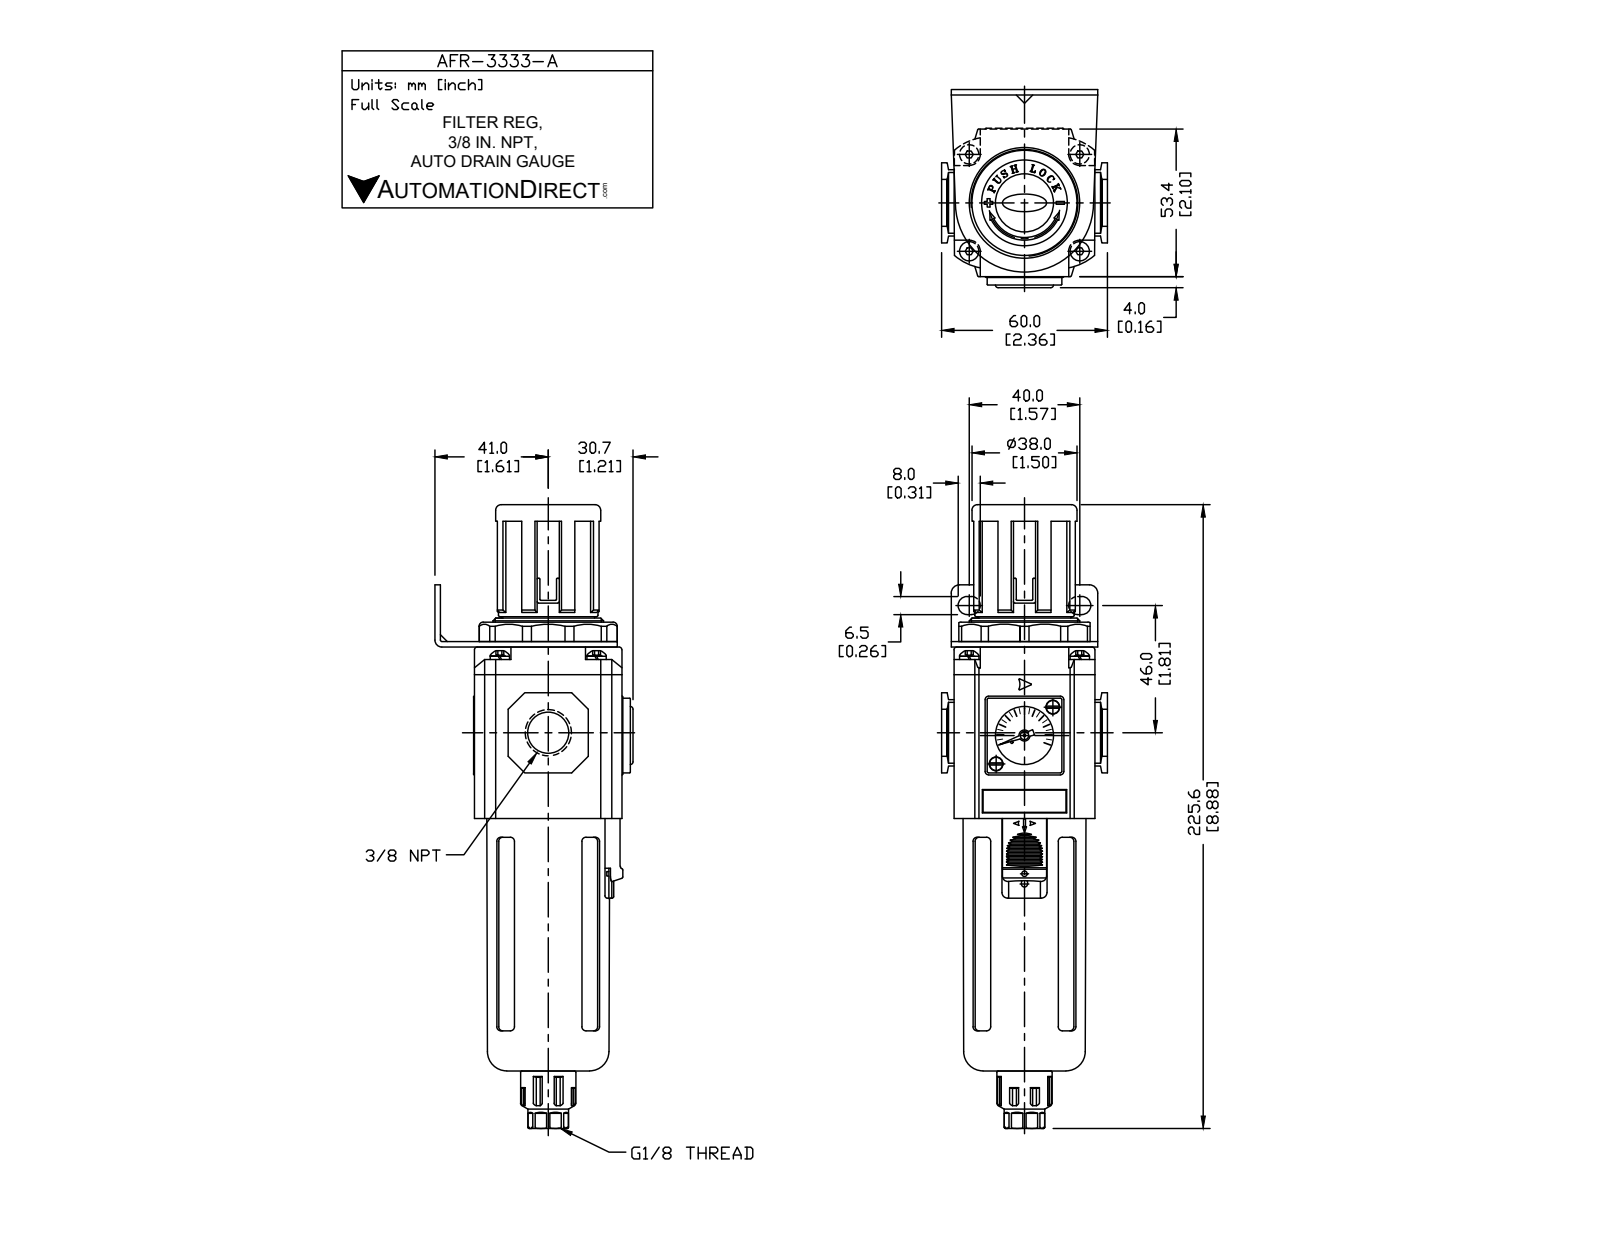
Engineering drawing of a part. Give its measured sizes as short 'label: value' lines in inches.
name: AFR-3333-A
written by: SolidWorks 2015 (CONFIG_CONTROL_DESIGN)
unit: in
bodies: 16 solids, 606 faces (370 planar, 172 cylindrical, 64 other)
size: 8.882 × 2.835 × 2.362
volume: 16.68 in³; area: 108.8 in²
holes: 6× ⌀0.118, 1× ⌀0.079, 1× ⌀0.244, 1× ⌀0.562, 1× ⌀0.63, 1× ⌀0.827, 1× ⌀1.181, 1× ⌀1.26, 1× ⌀1.386
bosses: 4× ⌀0.217, 2× ⌀0.106, 1× ⌀1.732, 1× ⌀1.575, 1× ⌀1.496, 1× ⌀1.417, 1× ⌀1.319, 1× ⌀0.806
rounds: 18× R0.087, 12× R0.039, 10× R0.047, 8× R0.02, 8× R0.374, 6× R0.128, 5× R0.157, 4× R0.012
face distances: 0.079, 2.441, 2.52, 2.102, 2.008, 1.559, 0.039, 2.185, 2.063, 0.177
hole spacings: 1.046, 0.571, 1.378, 1.575, 2.093, 1.141
